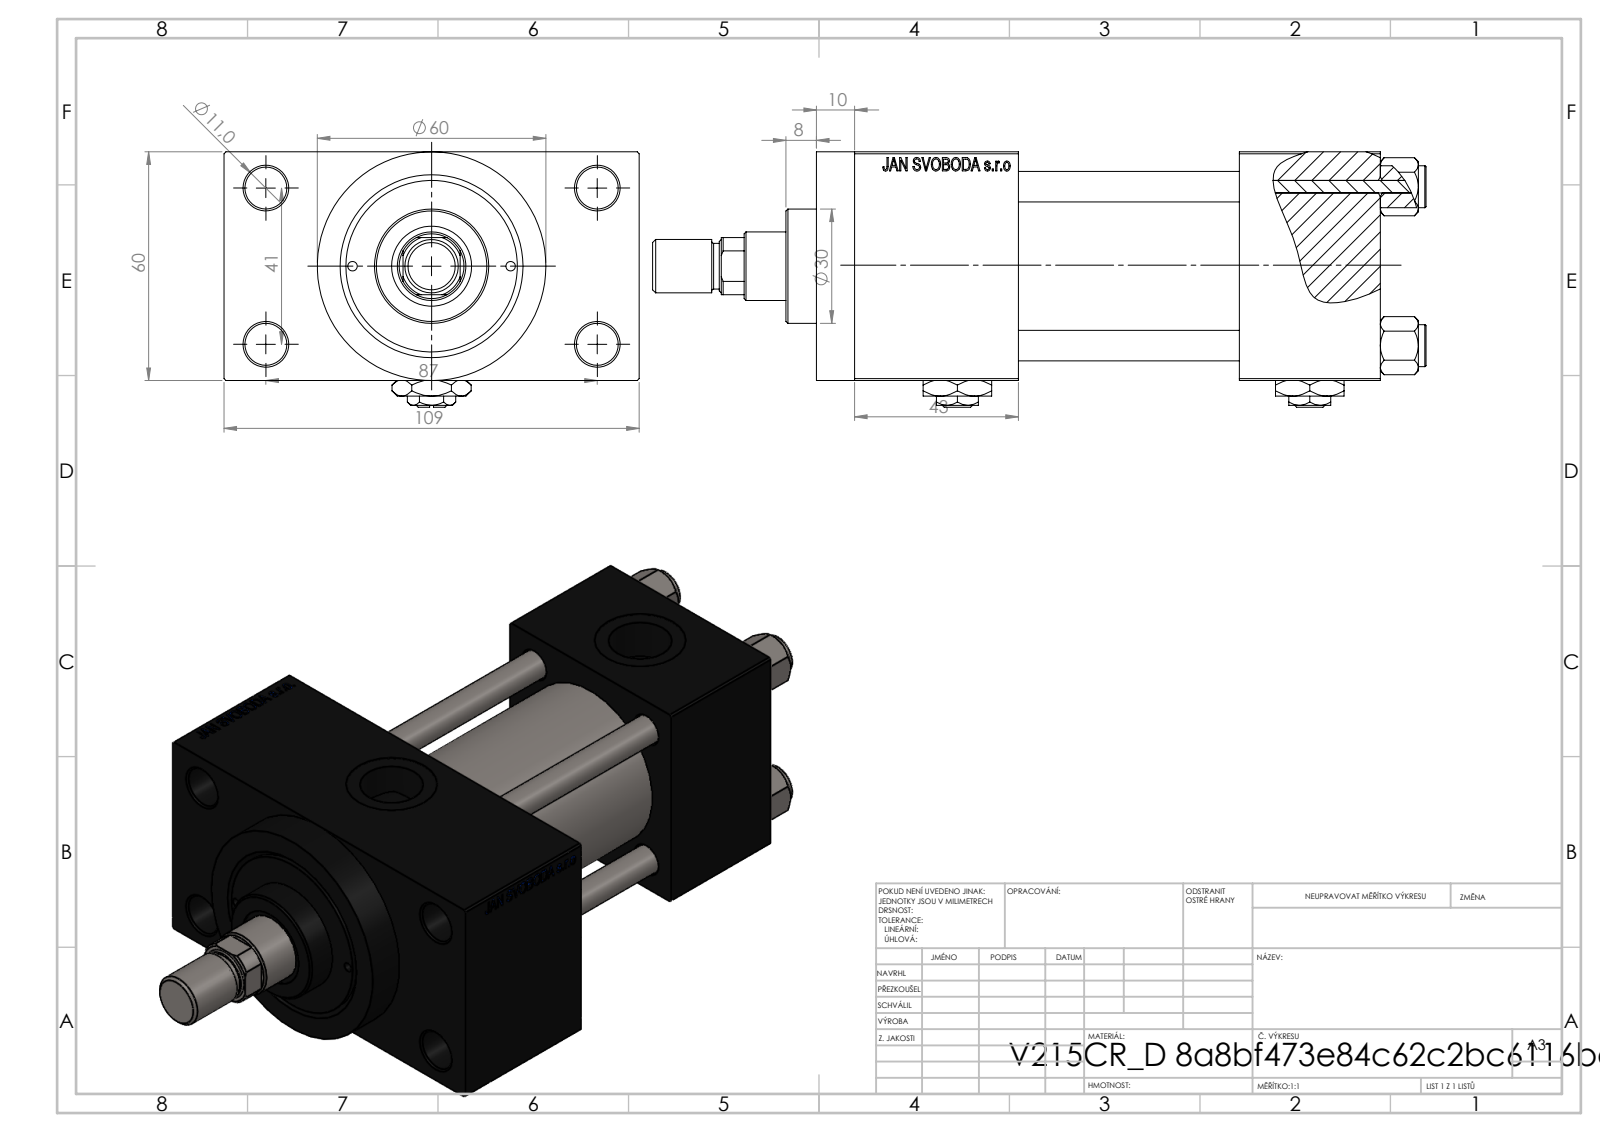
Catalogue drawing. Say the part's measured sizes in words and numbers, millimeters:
The part is named "NUT_M5_D; Zatka_pro_OIL_PORT; ROD_END_AH; V215CR_VCP_D (+3 more)". Its 3-D file was written by "SolidWorks 2019 (CONFIG_CONTROL_DESIGN)". It is 14 solids with 1228 faces: 552 planar, 108 cylindrical and 568 other. Overall it measures 203 by 109 by 67 millimeters. Its volume is 518 053 cubic millimeters and its surface area 124 998 square millimeters. Round holes: 4 of diameter 8, 4 of diameter 11, 2 of diameter 2.5, 2 of diameter 7, 2 of diameter 16.66, 2 of diameter 24, 1 of diameter 8.5, 1 of diameter 18, 1 of diameter 21, 1 of diameter 31, 1 of diameter 40, 1 of diameter 45. Round bosses or shafts: 4 of diameter 11, 1 of diameter 60, 1 of diameter 46, 1 of diameter 30, 1 of diameter 14, 1 of diameter 12. Partial cylindrical surfaces (rounded edges, fillets, slot ends): 1 of radius 8.5. The main face-to-face distances are 60, 24.5, 84.5, 58, 37, 95, 43, 138, 101, 109. The hole center spacings are 20.85, 22.65, 29.49, 30.62, 41.7, 46.53, 47.15, 48.09.
